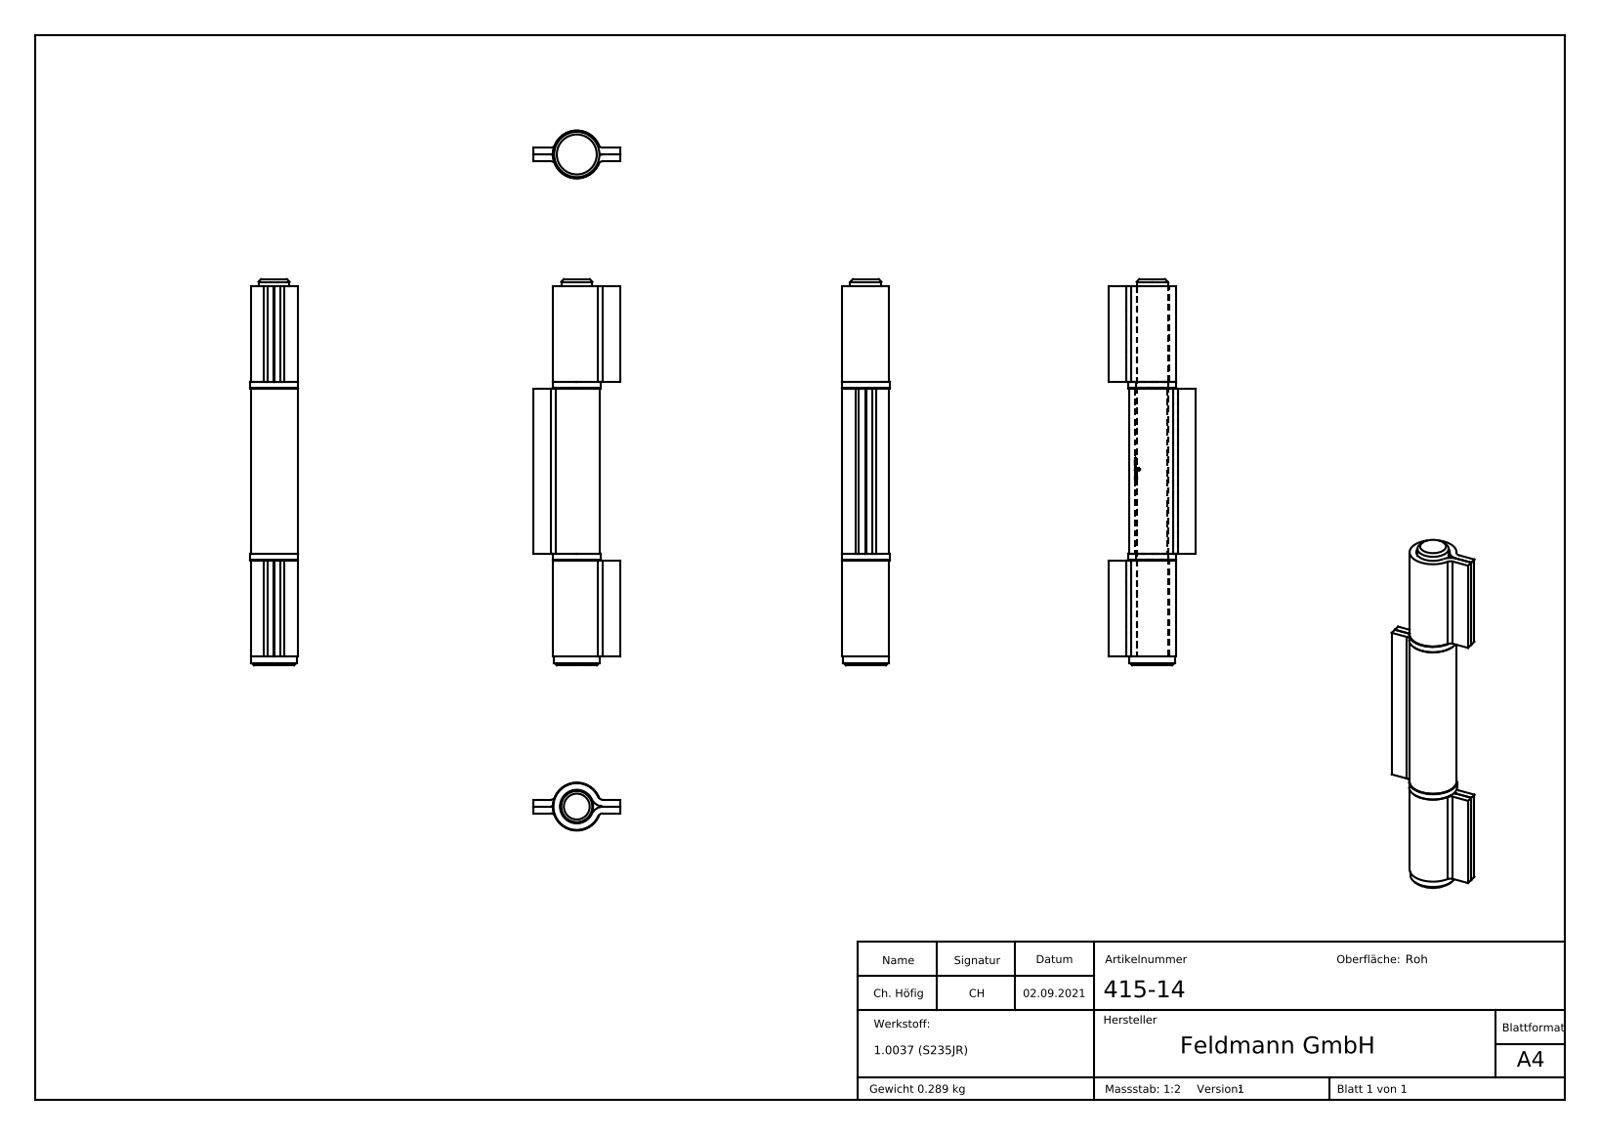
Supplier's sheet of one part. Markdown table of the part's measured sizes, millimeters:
| quantity | value |
| --- | --- |
| part name | 415-xx Teil1; 415-xx Teil4; 415-xx Teil1_415-14 Teil1; 415-xx Teil3 (+5 more) |
| STEP written by | SolidWorks 2018 (CONFIG_CONTROL_DESIGN) |
| units | millimeters |
| bodies | 6 solids, 285 faces (155 planar, 44 cylindrical, 86 other) |
| overall size | 145 × 32.4 × 18 |
| volume | 37 127 mm³ |
| surface area | 24 769 mm² |
| round holes (diameter × count) | 12 × 1, 12.6 × 1 |
| round bosses / shafts (diameter × count) | 18 × 1, 17.6 × 1, 17 × 1, 11.7 × 1 |
| partial cylindrical surfaces (radius × count) | 2 × 4, 4.5 × 4, 6.4 × 1 |
| main face-to-face distances | 2.5, 2.6, 5.1, 64.5, 38.5, 103, 36, 100.5, 32.4, 67 |
